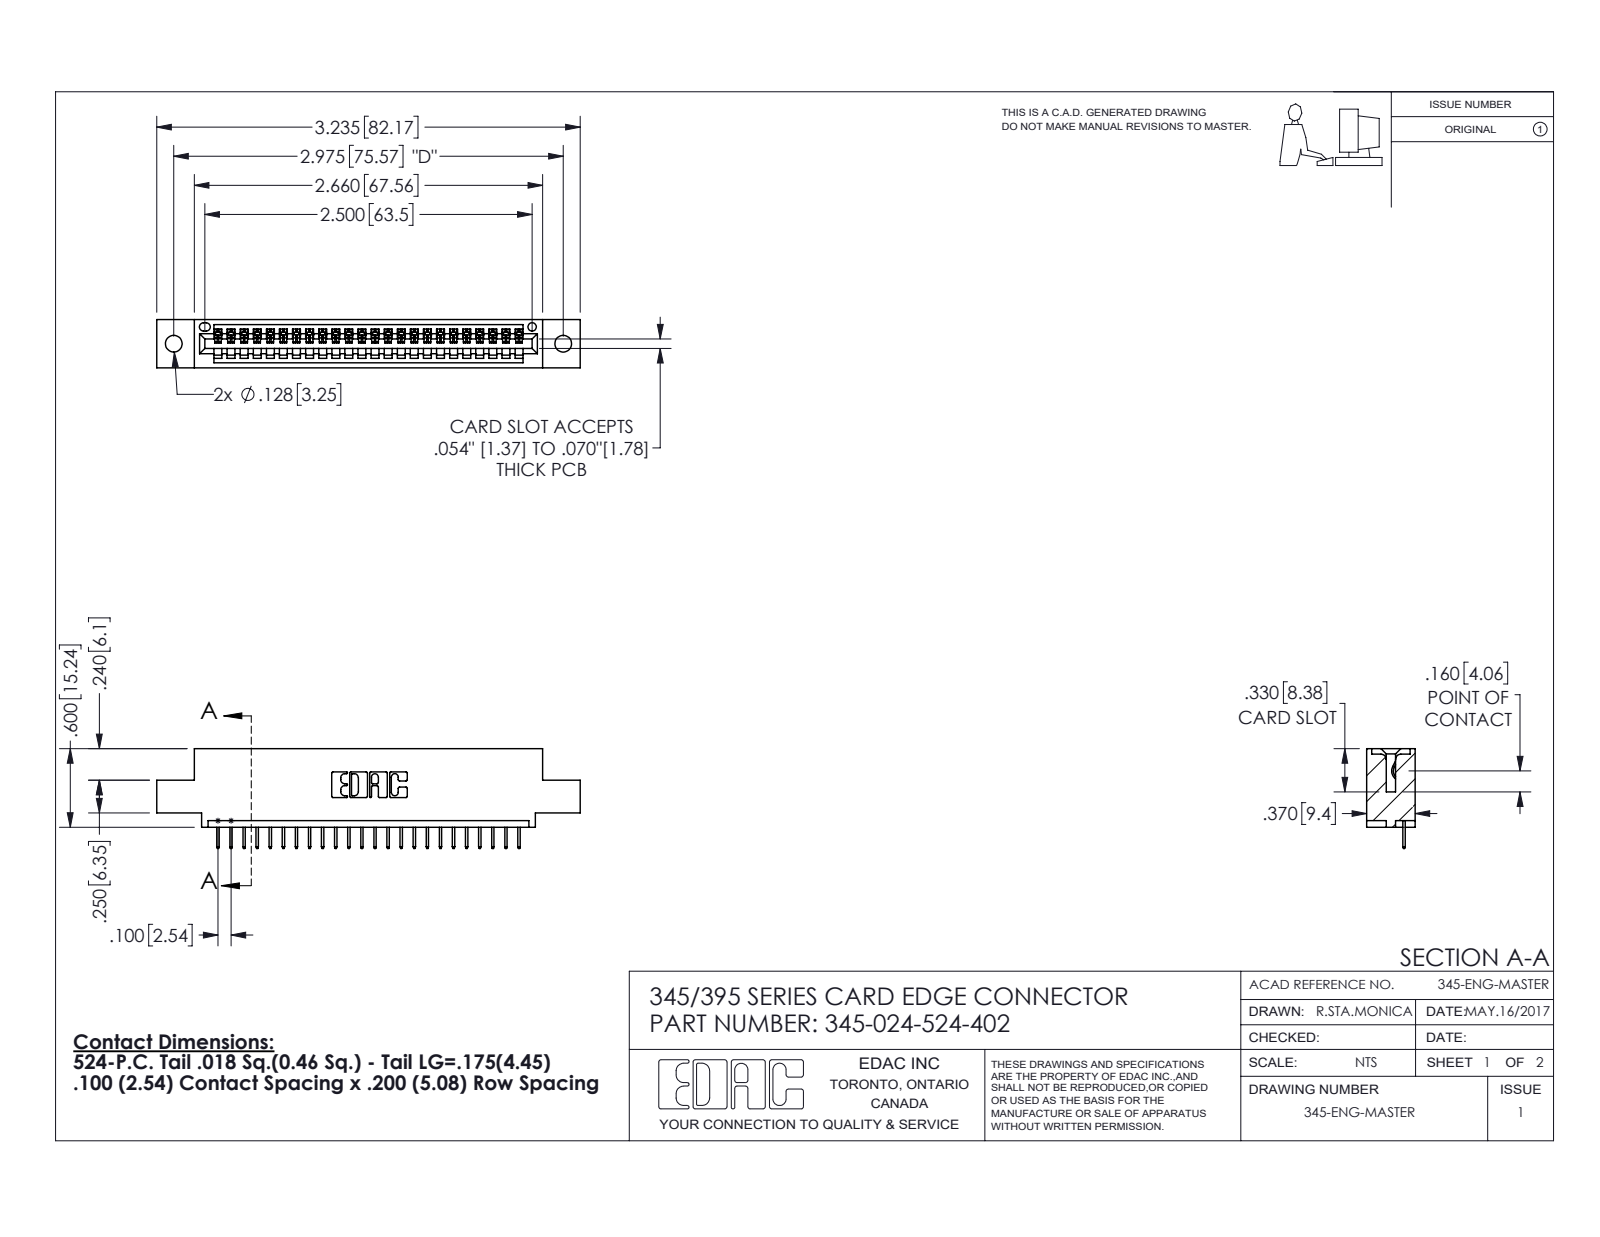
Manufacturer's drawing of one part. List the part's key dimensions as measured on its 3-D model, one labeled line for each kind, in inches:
Part name (STEP PRODUCT): 345-024-524-402; 345-292-001_345-293-124; 345 Part_0.110 Offset - 0.128 Dia
STEP written by: SolidWorks 2016 (CONFIG_CONTROL_DESIGN)
Units: inches
Bodies: 25 solids, 1618 faces (1188 planar, 430 cylindrical, 0 other)
Overall size (bounding box): 3.235 × 0.762 × 0.37
Volume: 0.455 in³ · Surface area: 14.21 in²
Round holes (diameter × count): ⌀0.128 ×2, ⌀0.064 ×1
Partial cylindrical surfaces — rounded edges, fillets, slot ends (radius × count): R0.006 ×48, R0.01 ×22, R0.007 ×6, R0.031 ×6, R0.026 ×3, R0.031 ×2, R0.04 ×2, R0.014 ×1
Main face-to-face distances: 0.072, 0.298, 0.37, 0.2, 0.098, 0.272, 0.025, 0.225, 0.072, 0.149
Hole centre spacings: 0.27, 2.741, 2.975
